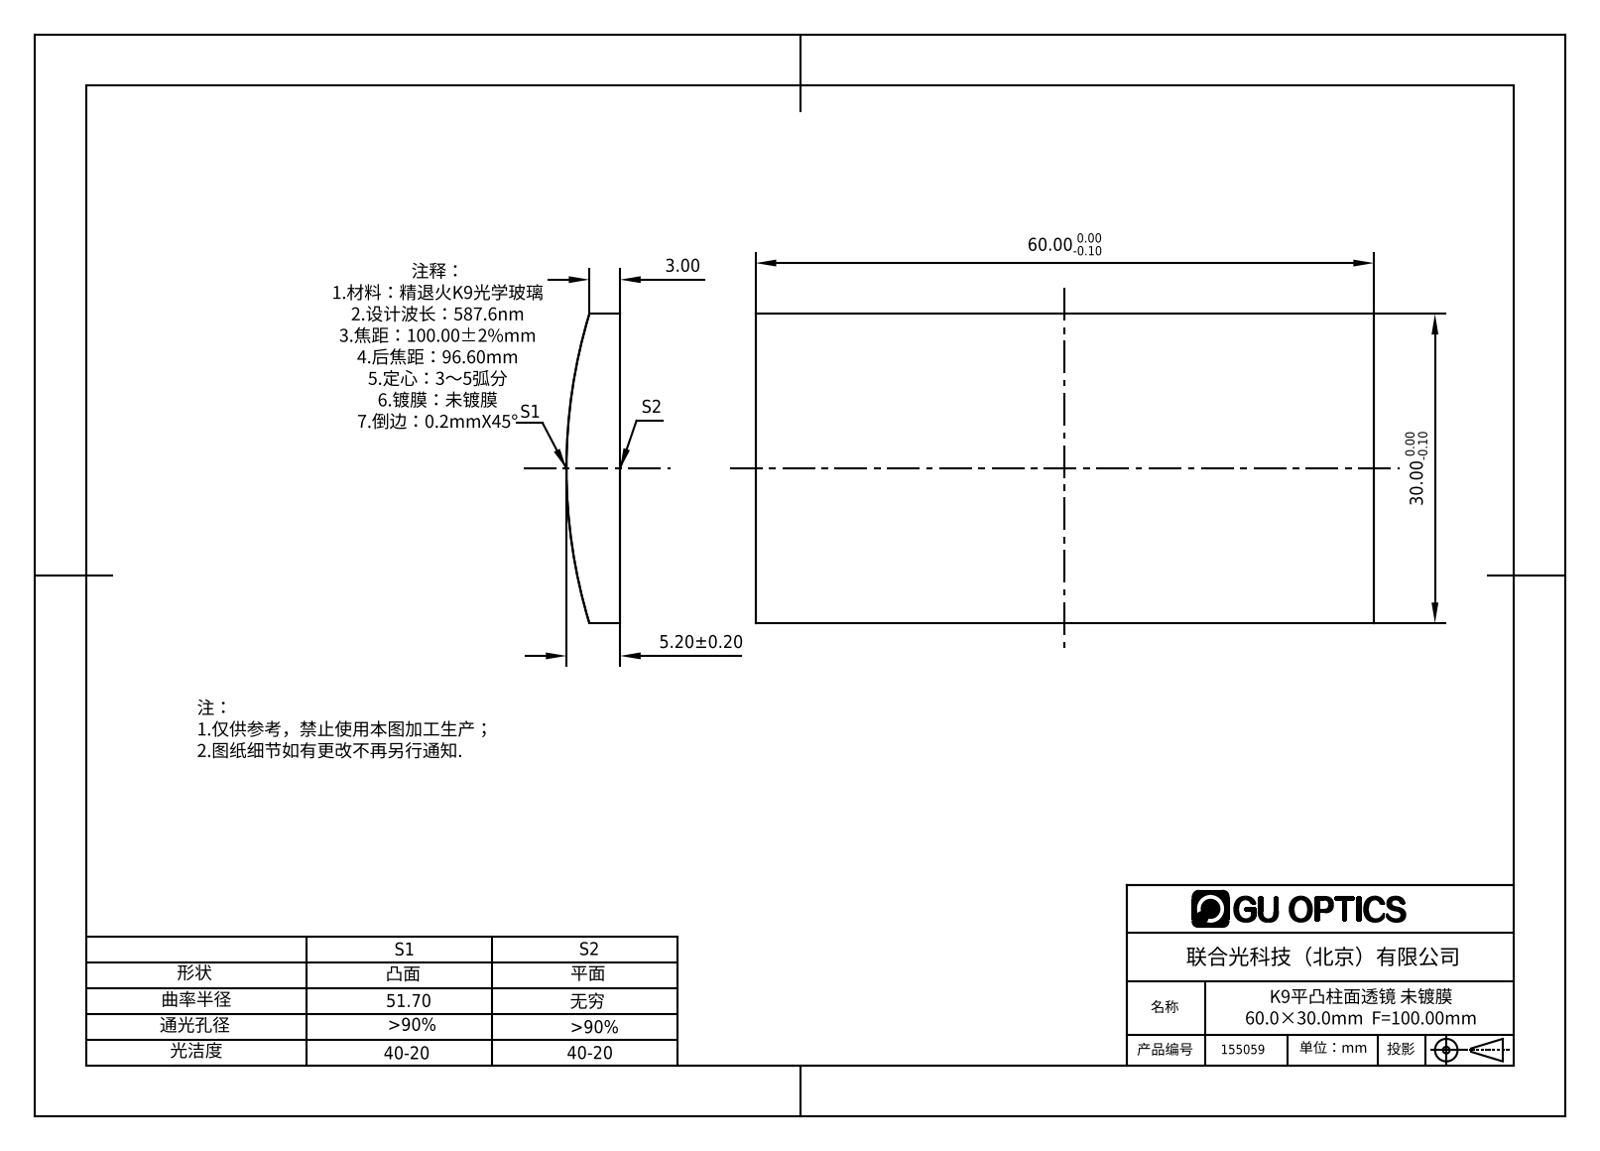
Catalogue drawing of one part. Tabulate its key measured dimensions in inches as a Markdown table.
| quantity | value |
| --- | --- |
| part name | 155059 |
| STEP written by | SolidWorks 2016 (AUTOMOTIVE_DESIGN) |
| units | inches |
| bodies | 1 solid, 6 faces (5 planar, 1 cylindrical, 0 other) |
| overall size | 2.362 × 1.181 × 0.205 |
| volume | 0.49 in³ |
| surface area | 6.589 in² |
| partial cylindrical surfaces (radius × count) | 2.035 × 1 |
| main face-to-face distances | 1.181, 2.362 |
